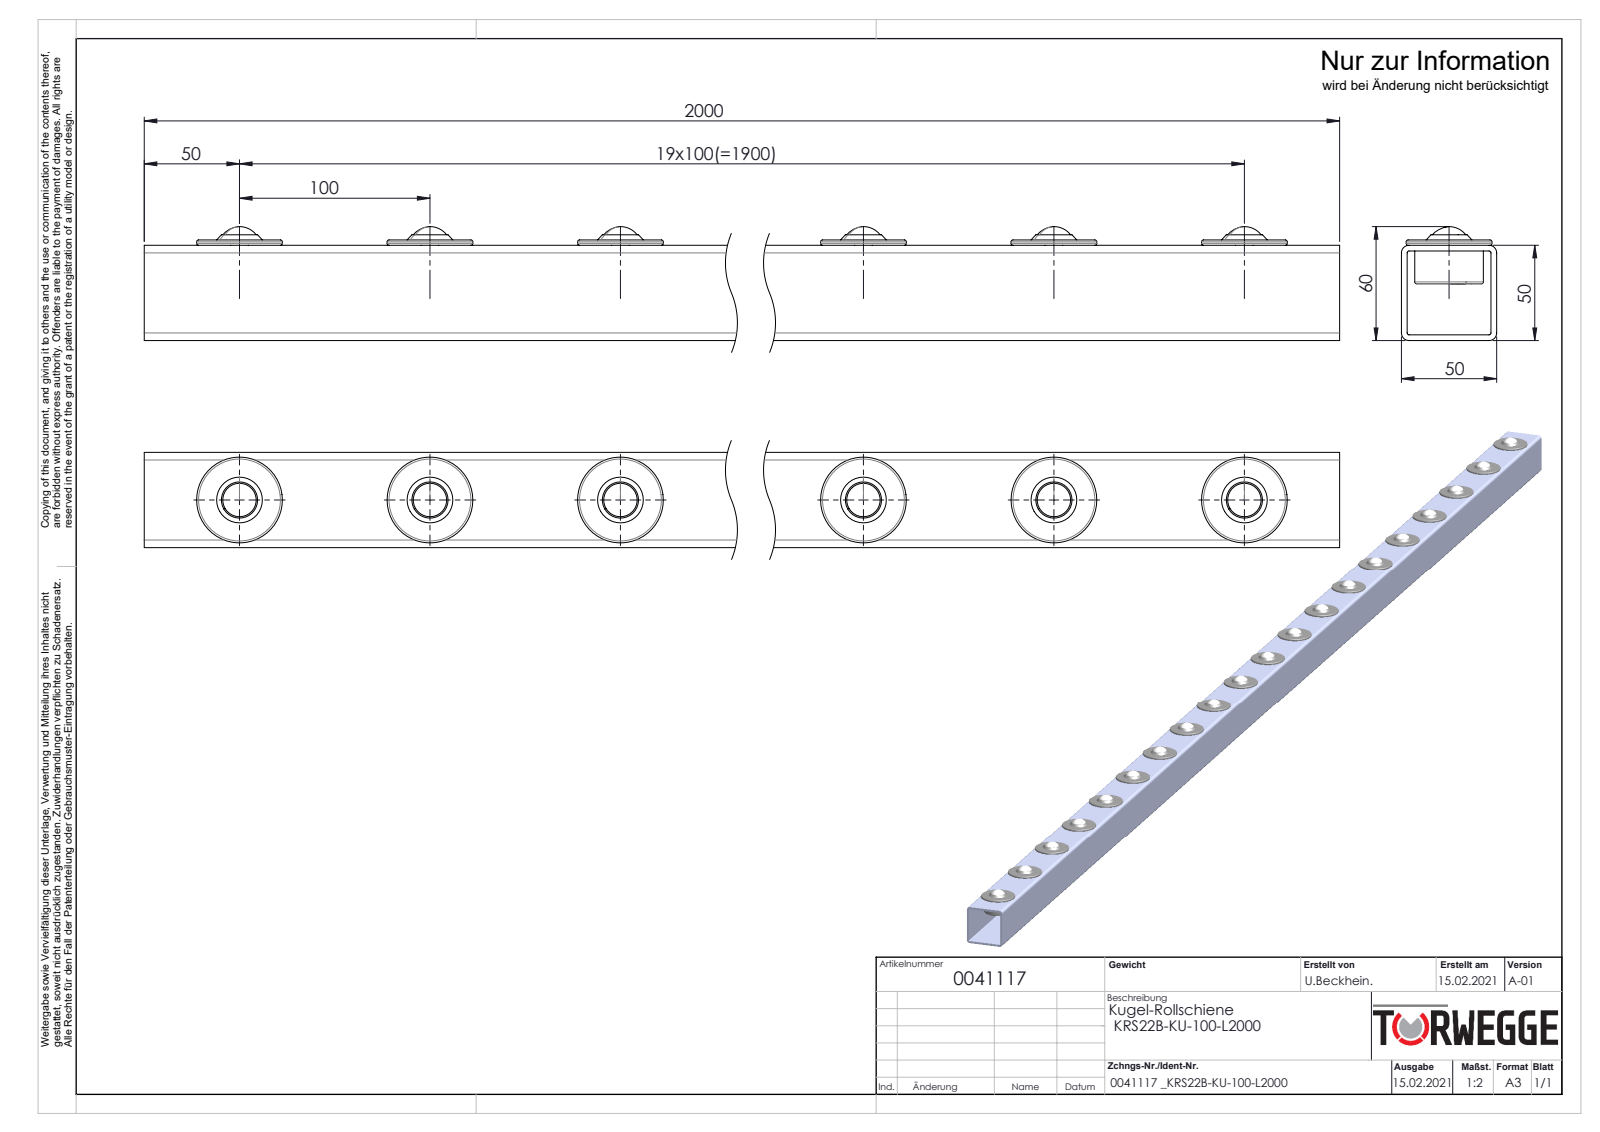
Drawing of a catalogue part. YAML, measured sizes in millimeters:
part_name: "0017493_KR-B-22-KU; 0041117; 0034065_VKR50x50x3_KFG_L2000-T100"
step_written_by: "SolidWorks 2020 (AUTOMOTIVE_DESIGN)"
units: millimeters
bodies: {solids: 21, faces: 838, planar: 110, cylindrical: 208, other: 520}
overall_size: [2000, 59.8, 50]
volume: 1545000
surface_area: 821563
round_holes:
  - {diameter: 2.5, count: 20}
  - {diameter: 7, count: 20}
  - {diameter: 36, count: 20}
round_bosses_or_shafts:
  - {diameter: 45, count: 20}
partial_cylinders:
  - {radius: 1, count: 4}
  - {radius: 4, count: 4}
face_to_face_distances: [3, 47, 50, 44, 52.8, 49.8, 5.8, 2.8, 55.5, 52.5]
hole_center_spacings: [100, 200, 300, 400, 500, 600, 700, 800]
